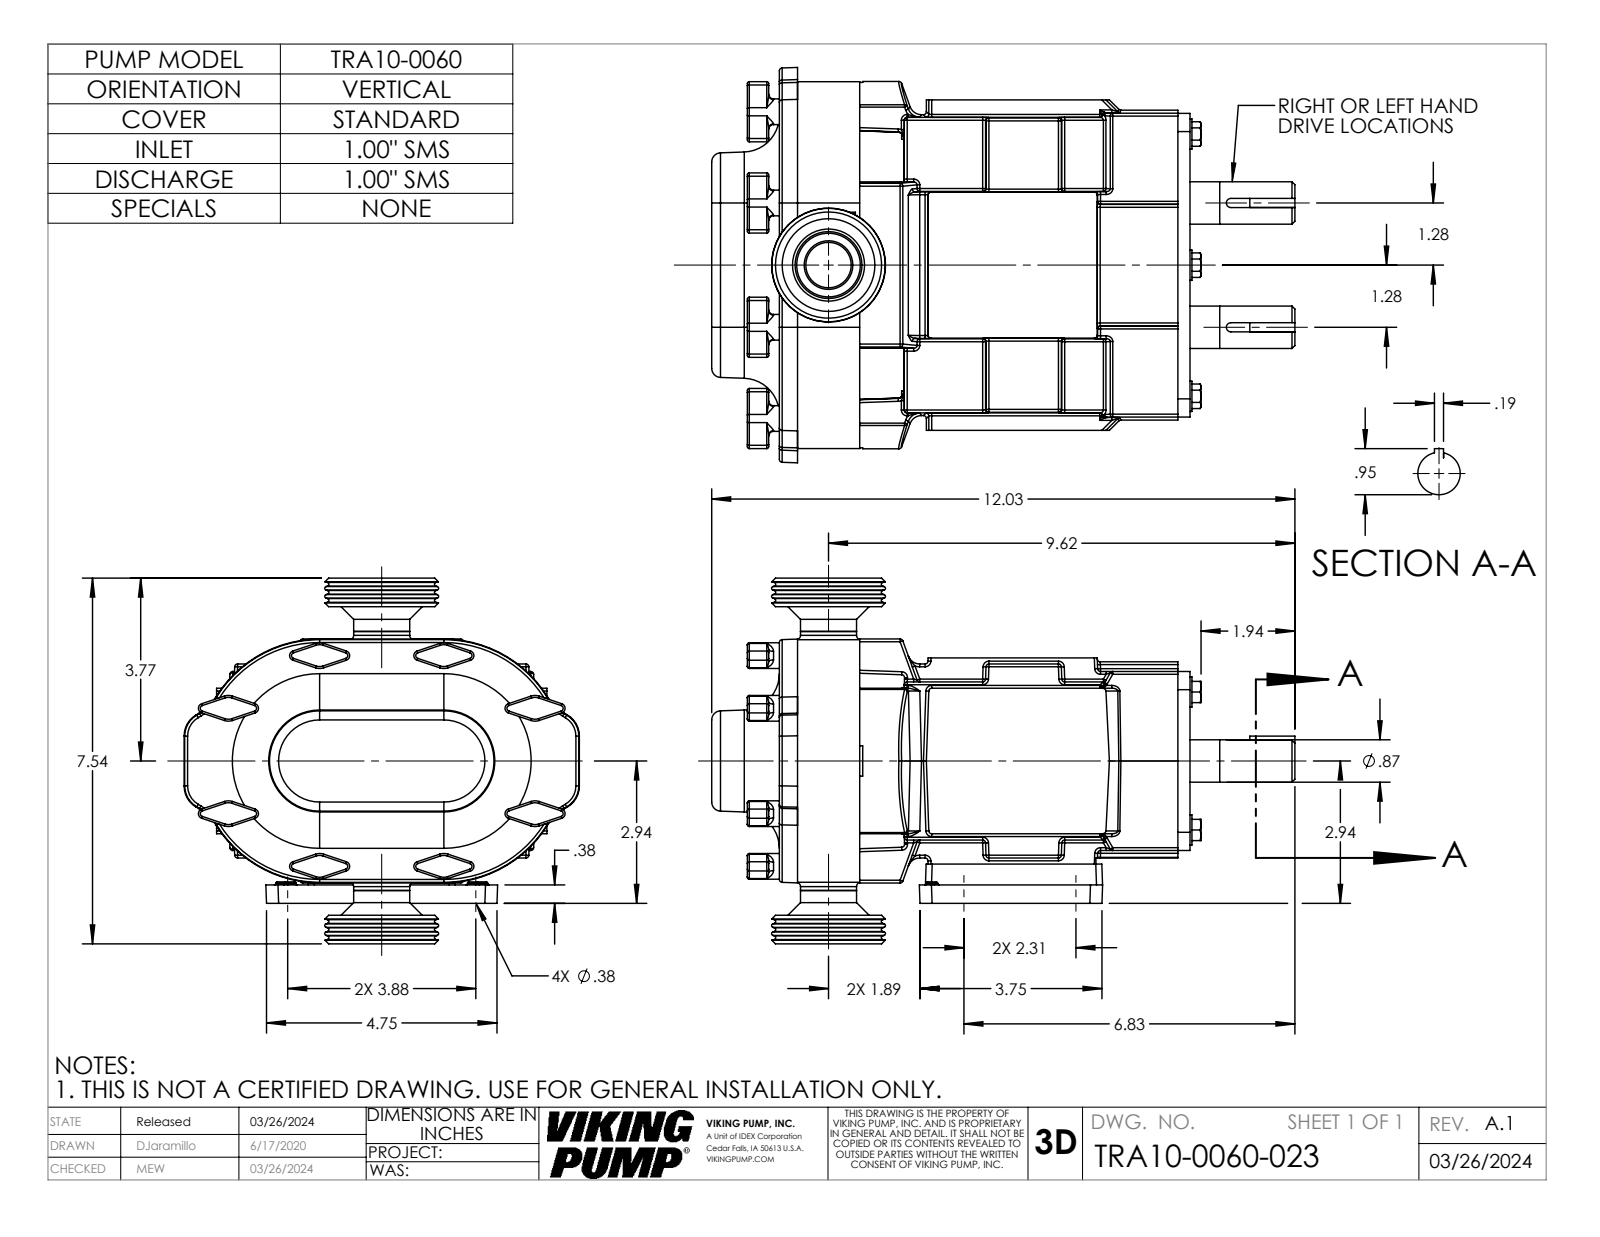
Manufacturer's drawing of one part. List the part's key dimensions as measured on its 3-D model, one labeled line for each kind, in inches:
Part name (STEP PRODUCT): TRA10-0150-GEARBOX-V; TRA10-0150-COVER-STD; TRA10-0150-BODY; 0150SMS15 (+1 more)
STEP written by: SolidWorks 2022 (AUTOMOTIVE_DESIGN)
Units: inches
Bodies: 5 solids, 1216 faces (314 planar, 429 cylindrical, 473 other)
Overall size (bounding box): 12.028 × 8.151 × 7.54
Volume: 241.7 in³ · Surface area: 497.2 in²
Round holes (diameter × count): ⌀0.375 ×4, ⌀0.937 ×1, ⌀1.38 ×1, ⌀1.912 ×1
Round bosses / shafts (diameter × count): ⌀0.53 ×8, ⌀0.625 ×6, ⌀0.874 ×2, ⌀1.486 ×1, ⌀1.156 ×1
Partial cylindrical surfaces — rounded edges, fillets, slot ends (radius × count): R0.06 ×175, R0.04 ×64, R0.03 ×16, R0.1 ×16, R0.25 ×14, R0.125 ×12, R0.375 ×4, R0.5 ×4
Main face-to-face distances: 1.282, 6.813, 8.094, 5.687, 1.125, 2.407, 0.375, 0.215, 3.475, 8.47
Hole centre spacings: 2.31, 3.88, 4.516, 3.4, 3.401, 5.459, 5.46
